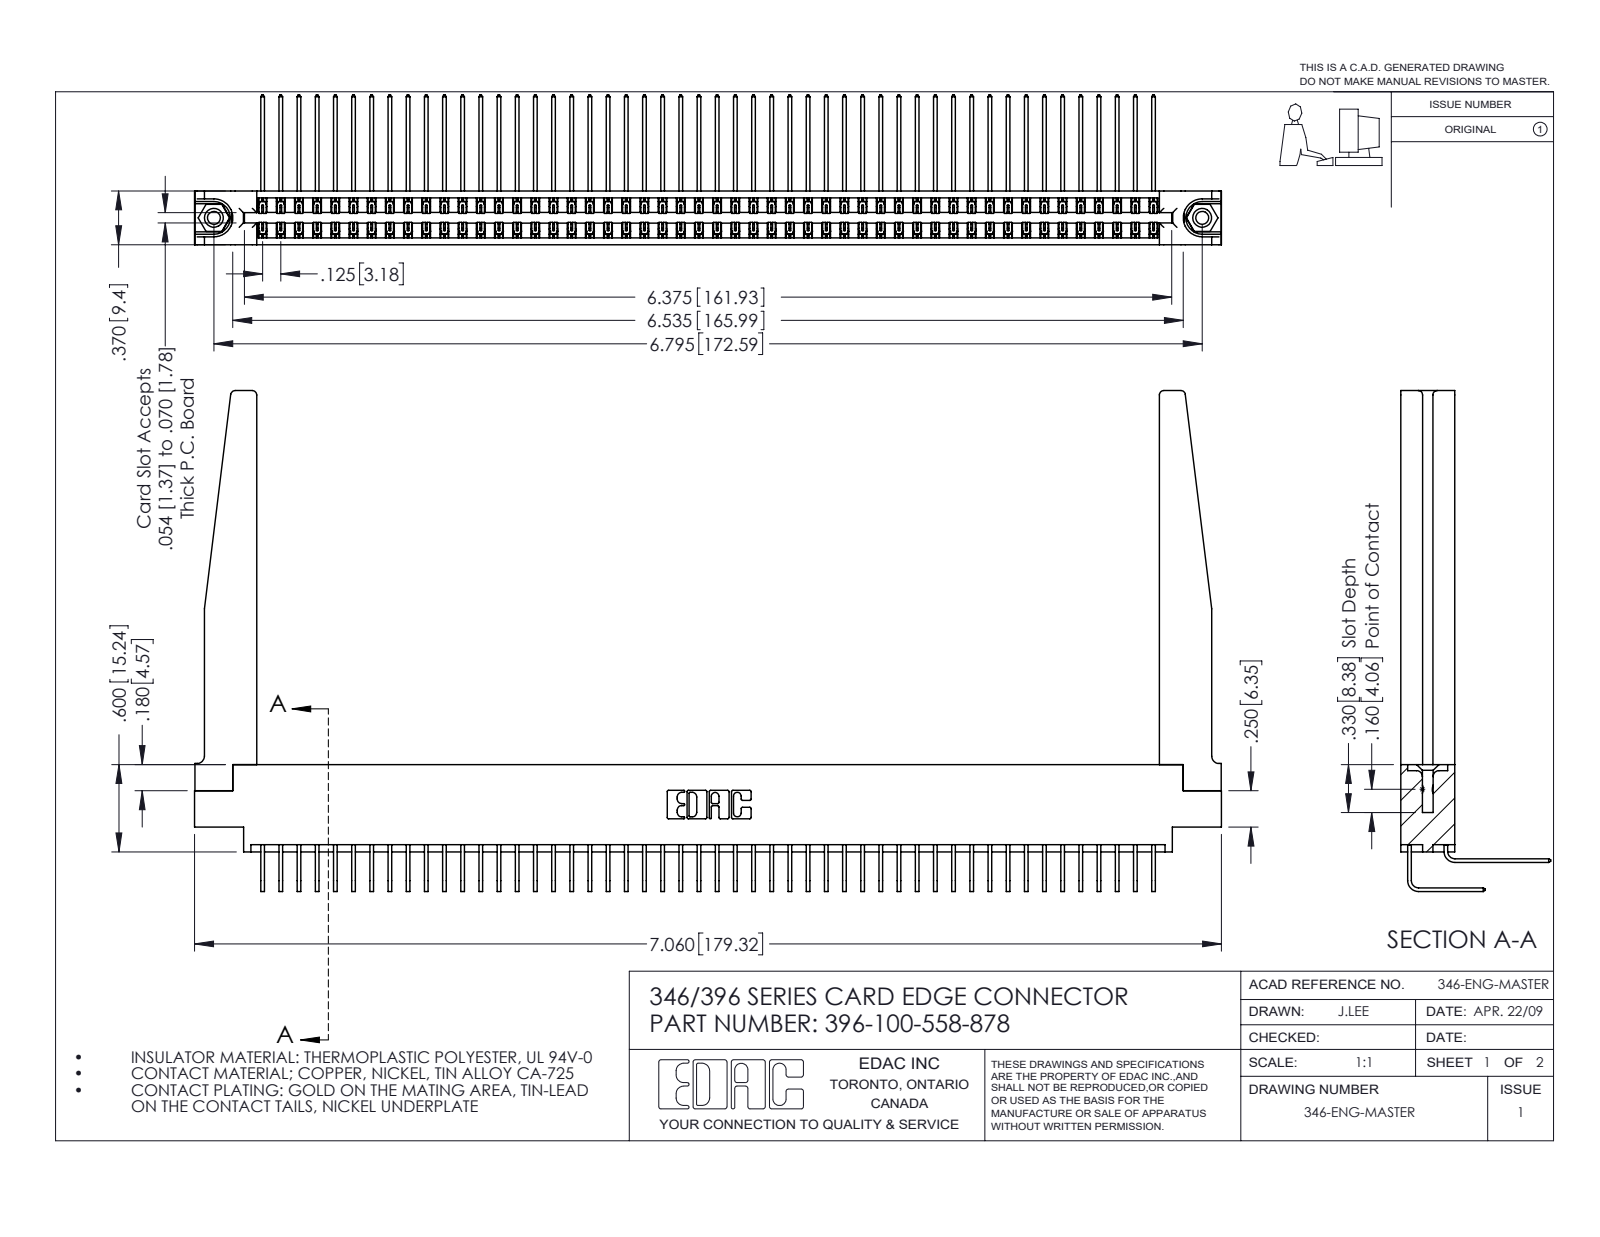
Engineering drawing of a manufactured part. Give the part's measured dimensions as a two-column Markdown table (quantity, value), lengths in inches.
| quantity | value |
| --- | --- |
| part name | 345-292-001_558 Tail - 2; 396-100-558-878; 346 Part_0.170 Offset - 0.156 Dia-TH; 346-220-078_345-220-078 (+2 more) |
| STEP written by | SolidWorks 2016 (CONFIG_CONTROL_DESIGN) |
| units | inches |
| bodies | 105 solids, 5760 faces (3922 planar, 1786 cylindrical, 52 other) |
| overall size | 7.06 × 3.443 × 1.03 |
| volume | 1.518 in³ |
| surface area | 53.18 in² |
| round holes (diameter × count) | 0.089 × 2, 0.125 × 2, 0.156 × 2, 0.064 × 1 |
| round bosses / shafts (diameter × count) | 0.155 × 2 |
| partial cylindrical surfaces (radius × count) | 0.006 × 150, 0.01 × 22, 0.03 × 8, 0.007 × 6, 0.031 × 6, 0.05 × 4, 0.026 × 3, 0.014 × 2 |
| main face-to-face distances | 0.322, 0.048, 0.37, 0.072, 0.025, 0.298, 0.25, 0.148, 0.15, 0.275 |
| hole center spacings | 0.246, 6.586, 6.795 |
